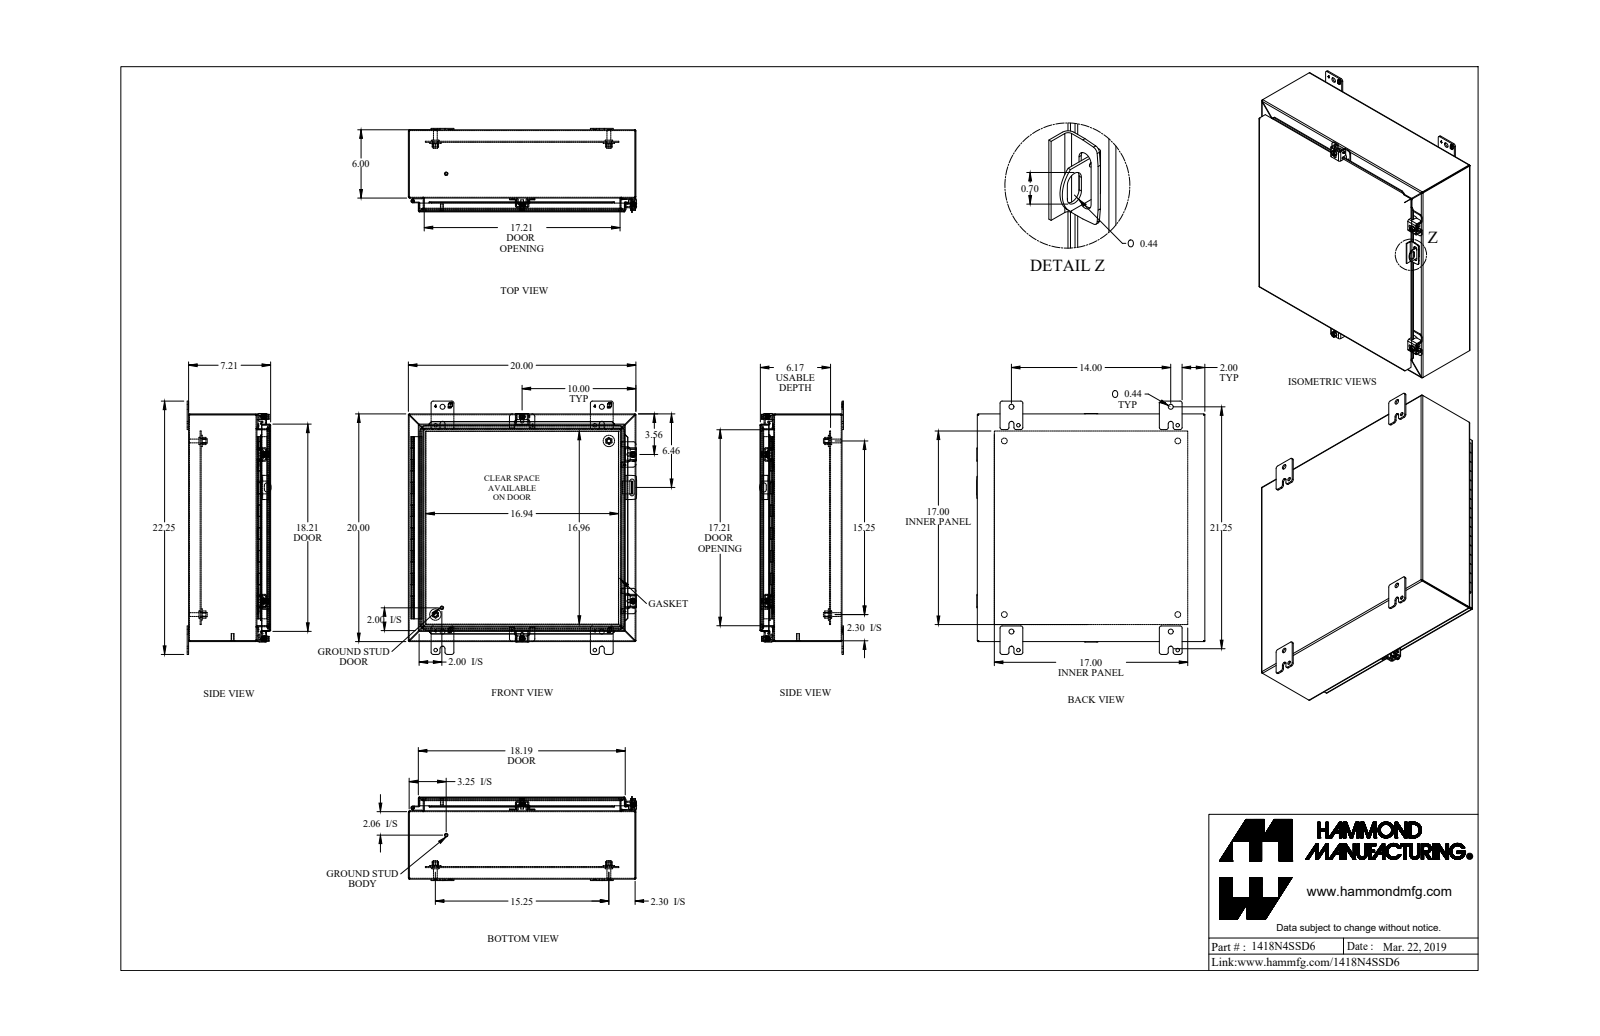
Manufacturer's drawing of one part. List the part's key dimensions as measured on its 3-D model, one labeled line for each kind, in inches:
Part name (STEP PRODUCT): 1418N4SSD6_Default
STEP written by: SolidWorks 2019 (CONFIG_CONTROL_DESIGN)
Units: inches
Bodies: 39 solids, 1454 faces (905 planar, 457 cylindrical, 92 other)
Overall size (bounding box): 22.25 × 20.063 × 7.375
Volume: 145.5 in³ · Surface area: 3 835 in²
Round holes (diameter × count): ⌀0.213 ×4, ⌀0.265 ×4, ⌀0.313 ×4, ⌀0.375 ×4, ⌀0.437 ×4, ⌀0.5 ×4, ⌀0.307 ×2, ⌀0.445 ×2, ⌀0.125 ×1, ⌀0.187 ×1
Round bosses / shafts (diameter × count): ⌀0.65 ×4, ⌀0.5 ×4, ⌀0.39 ×4, ⌀0.375 ×4, ⌀0.332 ×4, ⌀0.244 ×4, ⌀1 ×2, ⌀0.313 ×2
Partial cylindrical surfaces — rounded edges, fillets, slot ends (radius × count): R0.188 ×26, R0.036 ×24, R0.108 ×24, R0.048 ×21, R0.143 ×21, R0.25 ×20, R0.045 ×8, R0.125 ×8
Main face-to-face distances: 0.072, 19.928, 7.066, 7.138, 7.138, 0.072, 7.21, 0.937, 1.009, 0.095
Hole centre spacings: 15.25, 7.916, 14, 18.975, 22.237, 2.434, 3.065, 16.762
